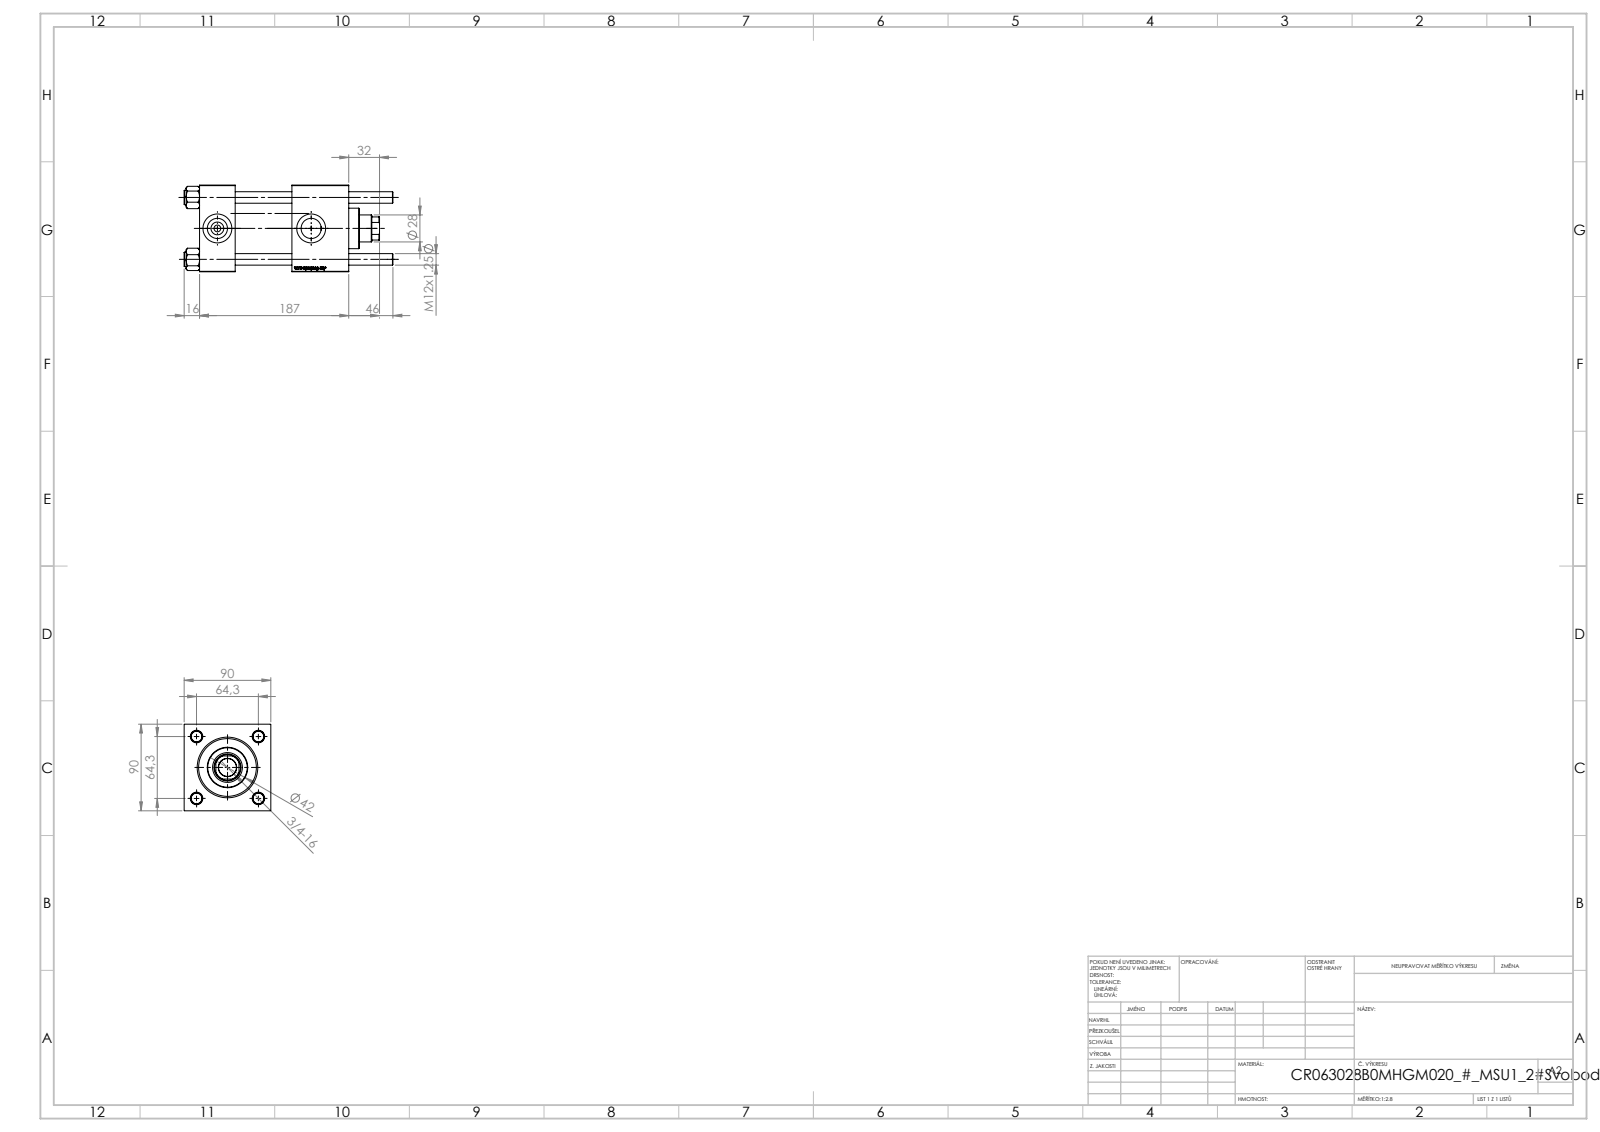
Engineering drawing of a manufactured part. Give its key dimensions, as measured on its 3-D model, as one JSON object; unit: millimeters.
{"part_name": "V215CR_B-1; V215CR_VCP_B; V215_VC_A; NUT_M5_B (+1 more)", "step_written_by": "SolidWorks 2019 (CONFIG_CONTROL_DESIGN)", "units": "millimeters", "bodies": {"solids": 11, "faces": 1158, "planar": 432, "cylindrical": 78, "other": 648}, "overall_size": [217, 90, 90], "volume_mm3": 981346, "surface_area_mm2": 195012, "round_holes": [[12, 4], [7, 2], [20.96, 2], [30, 2], [18.5, 1], [28, 1], [31, 1], [50, 1], [60, 1], [63, 1]], "round_bosses_or_shafts": [[15, 4], [69, 1], [42, 1]], "partial_cylinders_radius": [[13.5, 1]], "face_to_face_distances": [90, 59, 37, 155, 118, 96, 126.3, 89.3, 30.3, 28.7], "hole_center_spacings": [45.47, 64.3, 90.93, 97.5]}
